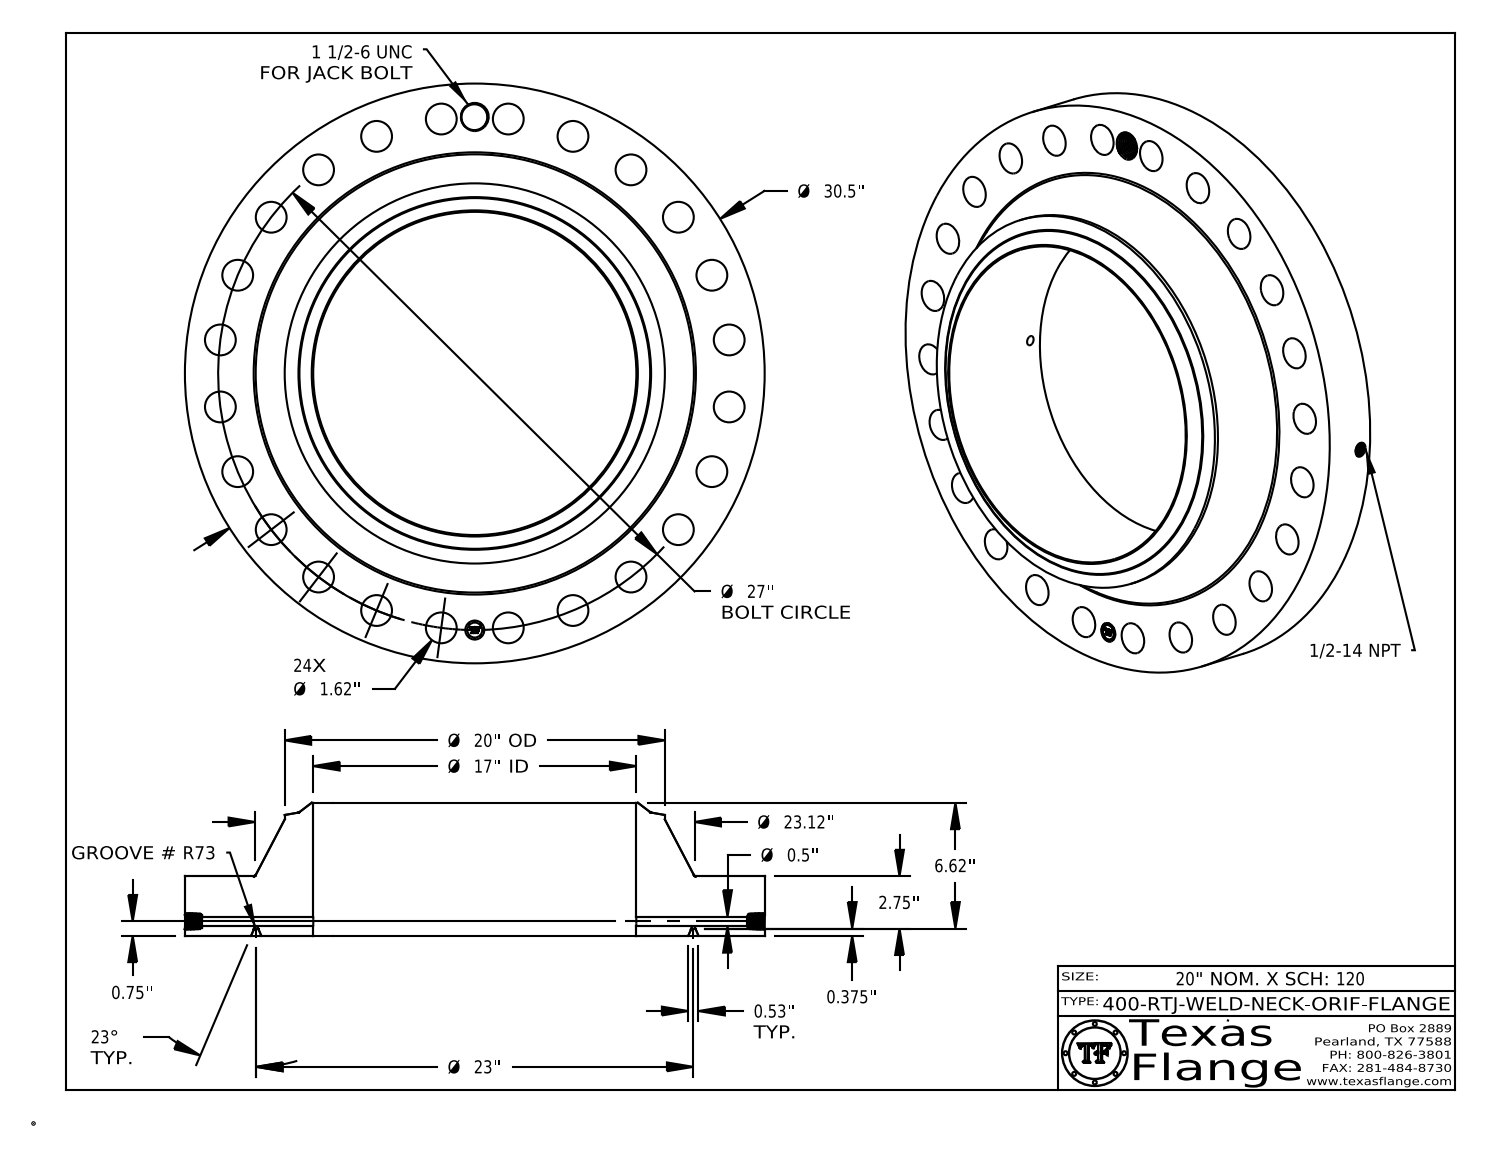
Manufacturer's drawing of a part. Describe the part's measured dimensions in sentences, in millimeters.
The part is named "400-RTJ-WELD-NECK". Its 3-D file was written by "CATIA V5 STEP AP214 (AUTOMOTIVE_DESIGN)". It is 1 solid with 835 faces: 370 planar, 131 cylindrical and 334 other. Overall it measures 774.7 by 774.7 by 177.7 millimeters. Its volume is 30 430 000 cubic millimeters and its surface area 1 410 000 square millimeters. Round holes: 24 of diameter 41.1, 1 of diameter 12.7, 1 of diameter 17.1, 1 of diameter 25.4, 1 of diameter 34.1, 1 of diameter 431.8. Round bosses or shafts: 8 of diameter 1.5, 1 of diameter 774.7, 1 of diameter 508, 1 of diameter 20. The main face-to-face distances are 79.4, 9.5, 69.9, 177.7, 168.1, 98.3, 0.4, 79, 69.5, 98.7. The hole center spacings are 342.9, 593.9, 633.6, 544.1, 89.5, 177.5, 484.9, 662.4.
